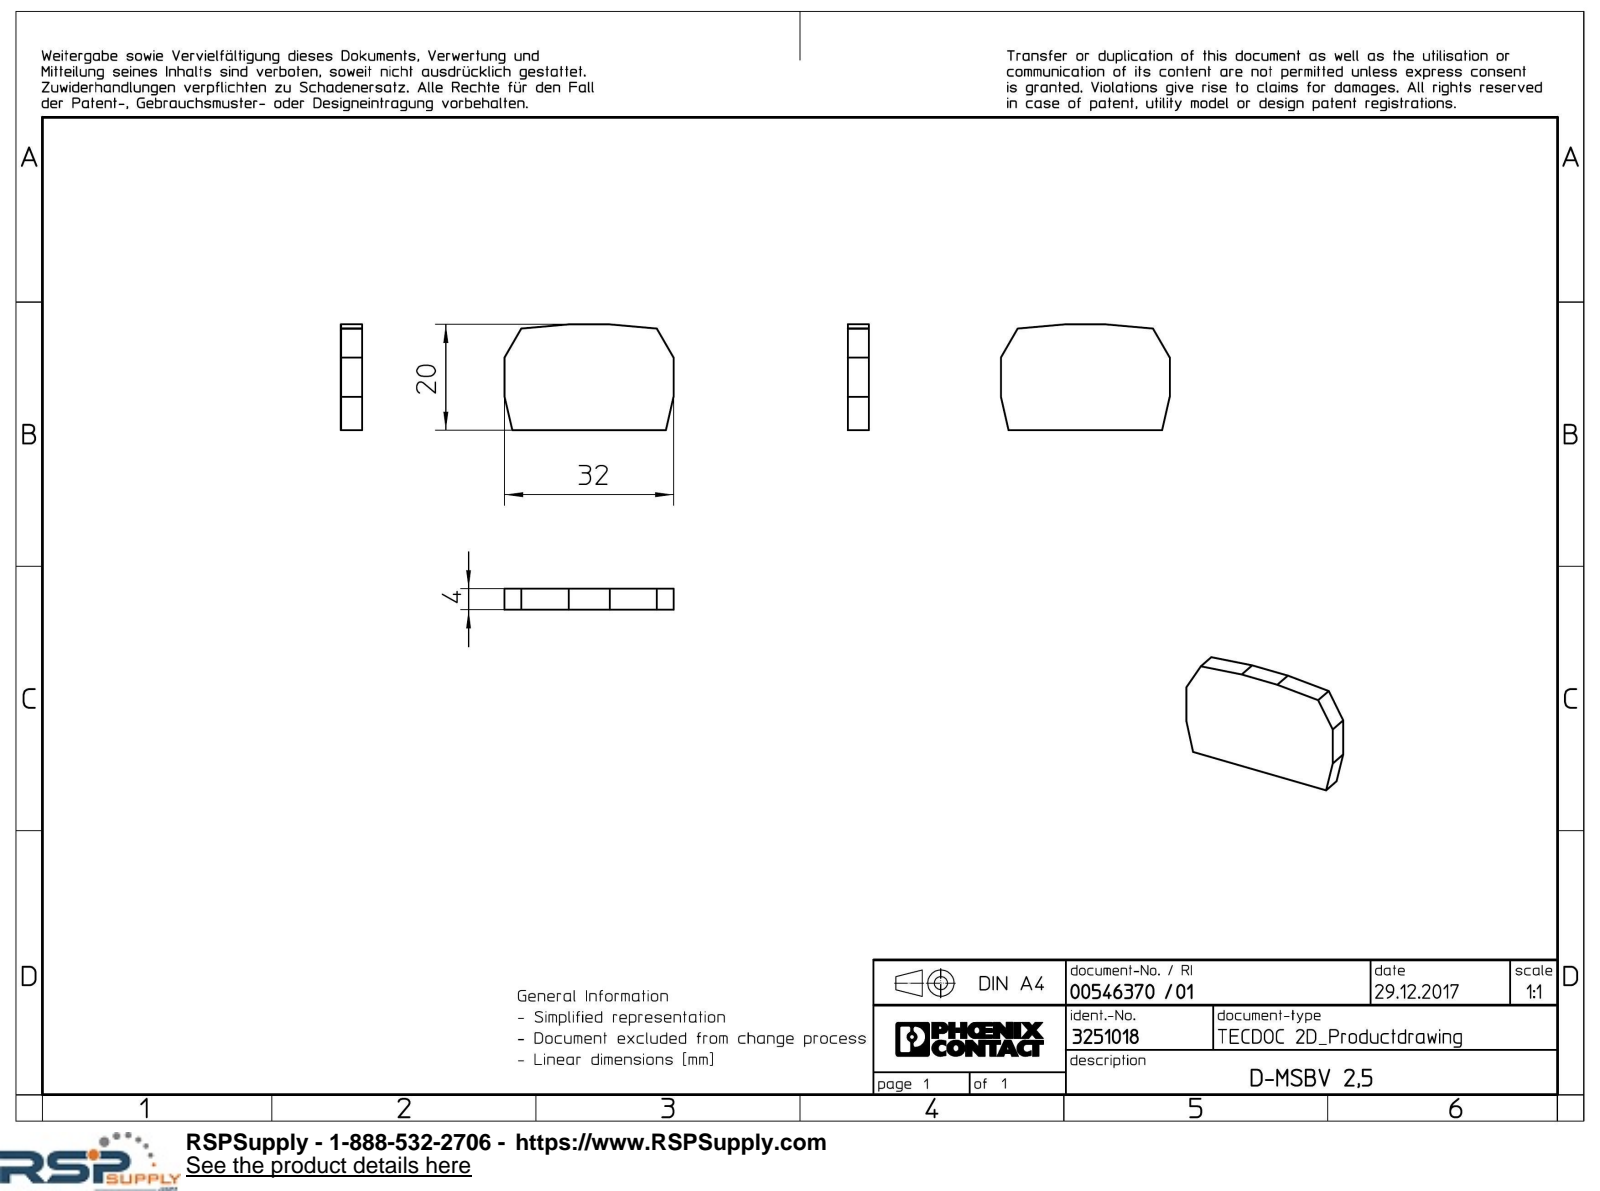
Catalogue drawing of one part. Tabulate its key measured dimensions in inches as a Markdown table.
| quantity | value |
| --- | --- |
| part name | D-MSBV_2.5-select |
| STEP written by | Creo Elements/Direct Modeling 18.1I 14-Aug-2016 (C) Parametric Technology GmbH (AUTOMOTIVE_DESIGN) |
| units | inches |
| bodies | 1 solid, 12 faces (12 planar, 0 cylindrical, 0 other) |
| overall size | 1.26 × 0.787 × 0.157 |
| volume | 0.147 in³ |
| surface area | 2.455 in² |
| main face-to-face distances | 0.157, 0.787, 1.26 |
